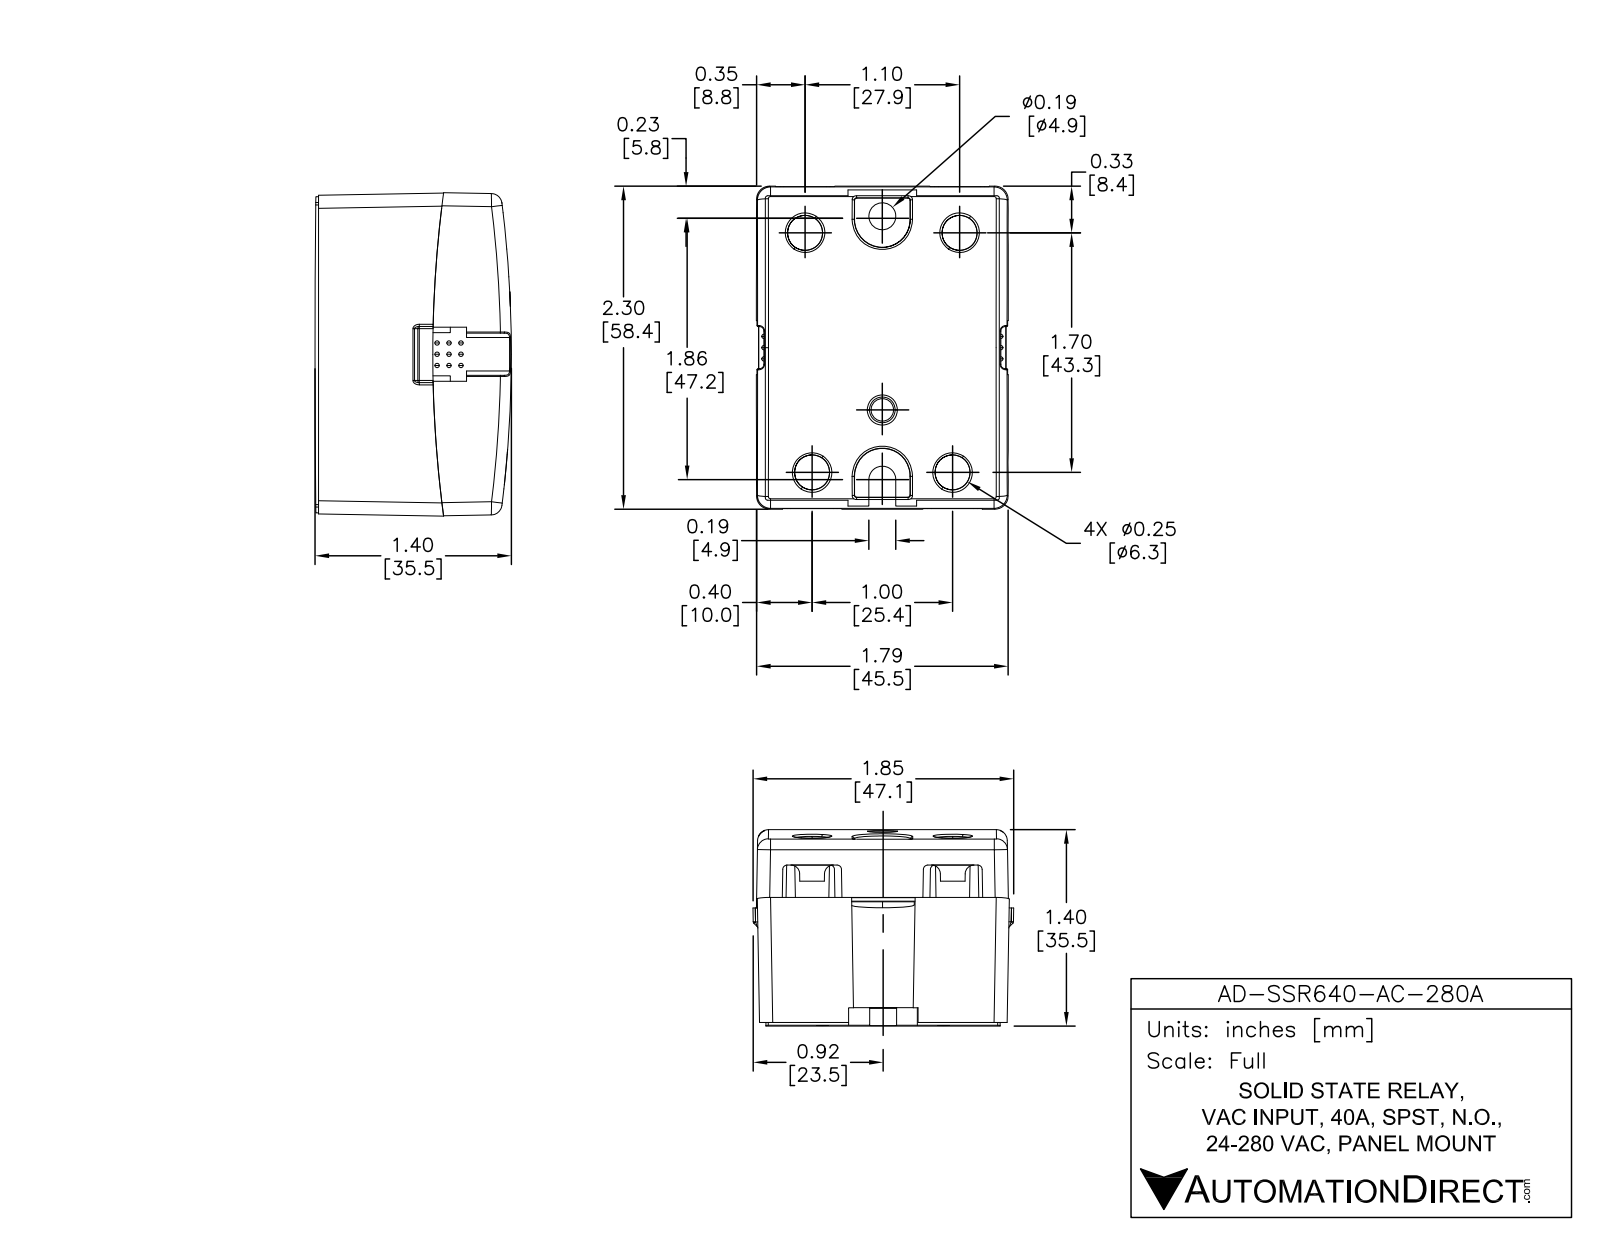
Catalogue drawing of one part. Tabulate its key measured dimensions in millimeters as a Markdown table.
| quantity | value |
| --- | --- |
| part name | AD-SSR640-AC-280A |
| STEP written by | SolidWorks 2013 (AUTOMOTIVE_DESIGN) |
| units | millimeters |
| bodies | 3 solids, 251 faces (145 planar, 95 cylindrical, 11 other) |
| overall size | 58.4 × 45.5 × 35.6 |
| volume | 84 230 mm³ |
| surface area | 17 040 mm² |
| round holes (diameter × count) | 6.4 × 4, 4.8 × 1 |
| round bosses / shafts (diameter × count) | 10.2 × 2, 8.9 × 2, 7.6 × 2, 6.4 × 2, 5.1 × 2, 5.1 × 2 |
| partial cylindrical surfaces (radius × count) | 0.8 × 6, 0.3 × 4, 1 × 4, 12.7 × 4, 4.9 × 2, 2.4 × 1, 12.7 × 1, 12.7 × 1 |
| main face-to-face distances | 45.5, 58.4, 29.6, 6.4, 23.3, 17, 26.9, 12.7, 45.7, 2 |
| hole center spacings | 14.1, 14.4, 25.4, 27.9, 43.2, 43.2, 47.7, 47.7 |
